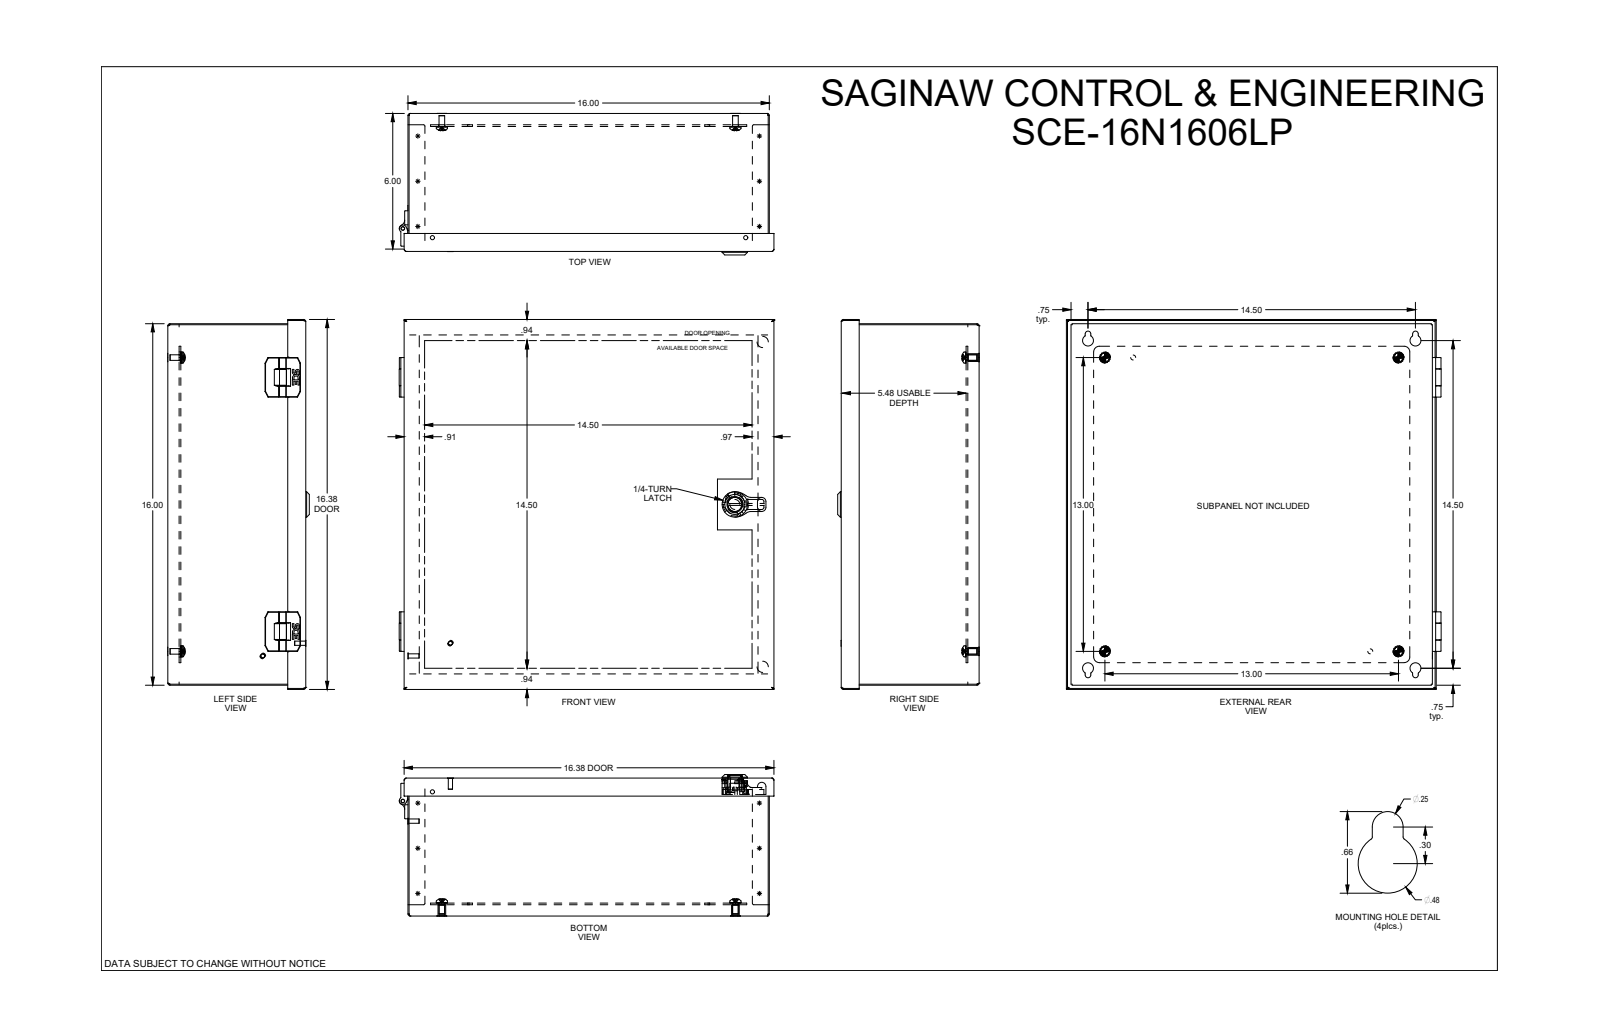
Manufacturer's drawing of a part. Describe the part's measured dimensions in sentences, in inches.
The part is named "SCE-16N1606LP". Its 3-D file was written by "SolidWorks 2019 (AUTOMOTIVE_DESIGN)". It is 31 solids with 1545 faces: 578 planar, 643 cylindrical and 324 other. Overall it measures 16.593 by 16.375 by 6.267 inches. Its volume is 75.08 cubic inches and its surface area 2 399 square inches. Round holes: 4 of diameter 0.17, 4 of diameter 0.25, 4 of diameter 0.281, 4 of diameter 0.329, 4 of diameter 0.343, 4 of diameter 0.48, 3 of diameter 0.193, 2 of diameter 0.187, 2 of diameter 0.218, 1 of diameter 0.158, 1 of diameter 0.44, 1 of diameter 0.635. Round bosses or shafts: 4 of diameter 0.492, 4 of diameter 0.479, 4 of diameter 0.341, 4 of diameter 0.248, 4 of diameter 0.237, 4 of diameter 0.16, 2 of diameter 0.5, 2 of diameter 0.323. Partial cylindrical surfaces (rounded edges, fillets, slot ends): 253 of radius 0.01, 95 of radius 0.02, 25 of radius 0.06, 24 of radius 0.015, 24 of radius 0.025, 6 of radius 0.055, 6 of radius 0.25, 4 of radius 0.125. The main face-to-face distances are 0.06, 6.047, 15.94, 5.987, 6.107, 0.5, 0.44, 0.575, 0.515, 5.472. The hole center spacings are 13.77, 1.061, 1.089, 1.091, 11.25, 13, 14.5, 19.445.
